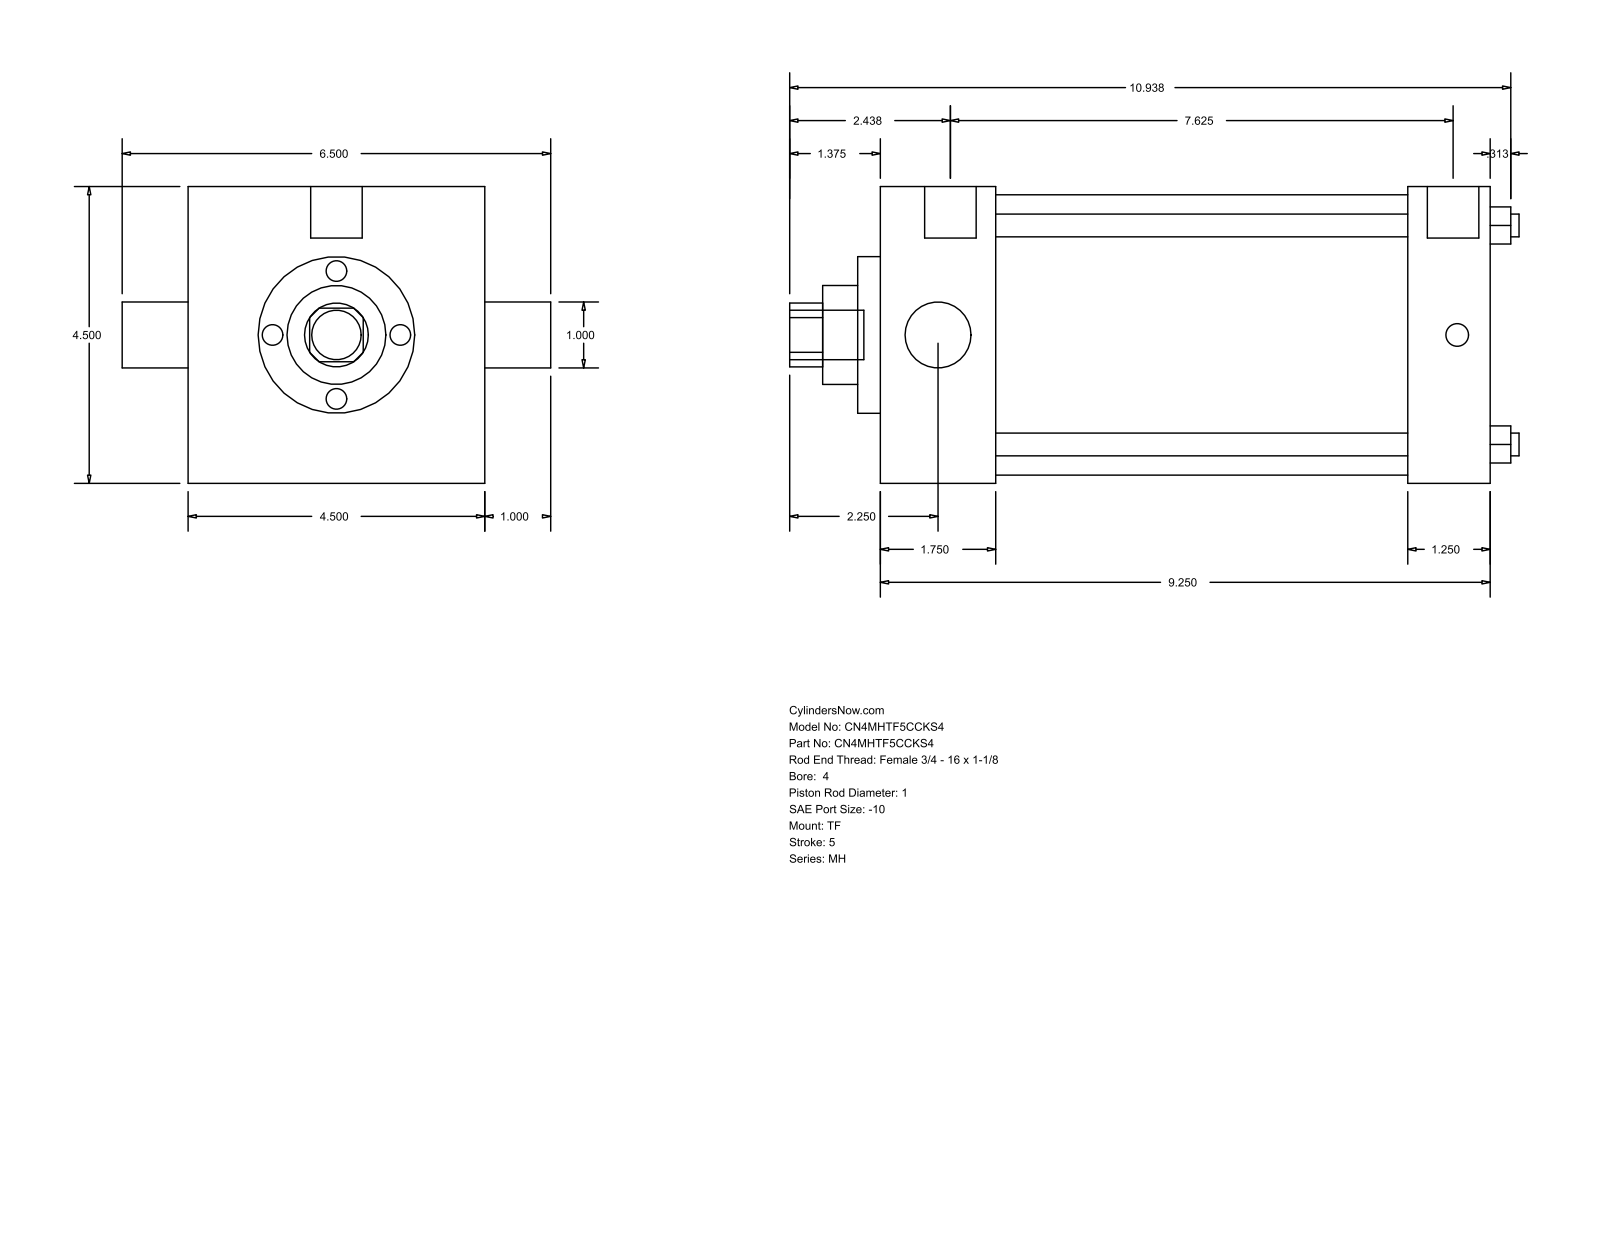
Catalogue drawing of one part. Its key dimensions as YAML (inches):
part_name: "MH_TF__0400_1"
step_written_by: "GSSL Pune (CONFIG_CONTROL_DESIGN)"
units: inches
bodies: {solids: 0, faces: 86, planar: 61, cylindrical: 25, other: 0}
overall_size: [11.063, 6.5, 4.5]
round_holes:
  - {diameter: 0.345, count: 4}
  - {diameter: 1, count: 2}
  - {diameter: 1.5, count: 1}
  - {diameter: 2.375, count: 1}
  - {diameter: 4.25, count: 1}
round_bosses_or_shafts:
  - {diameter: 0.344, count: 3}
  - {diameter: 0.781, count: 2}
  - {diameter: 0.75, count: 1}
partial_cylinders:
  - {radius: 0.484, count: 1}
face_to_face_distances: [4.5, 9.25, 1.75, 7.5, 8, 6.25, 1.25, 0.344, 2.094, 8.344]
hole_center_spacings: [2.347, 3.32, 4.695]
